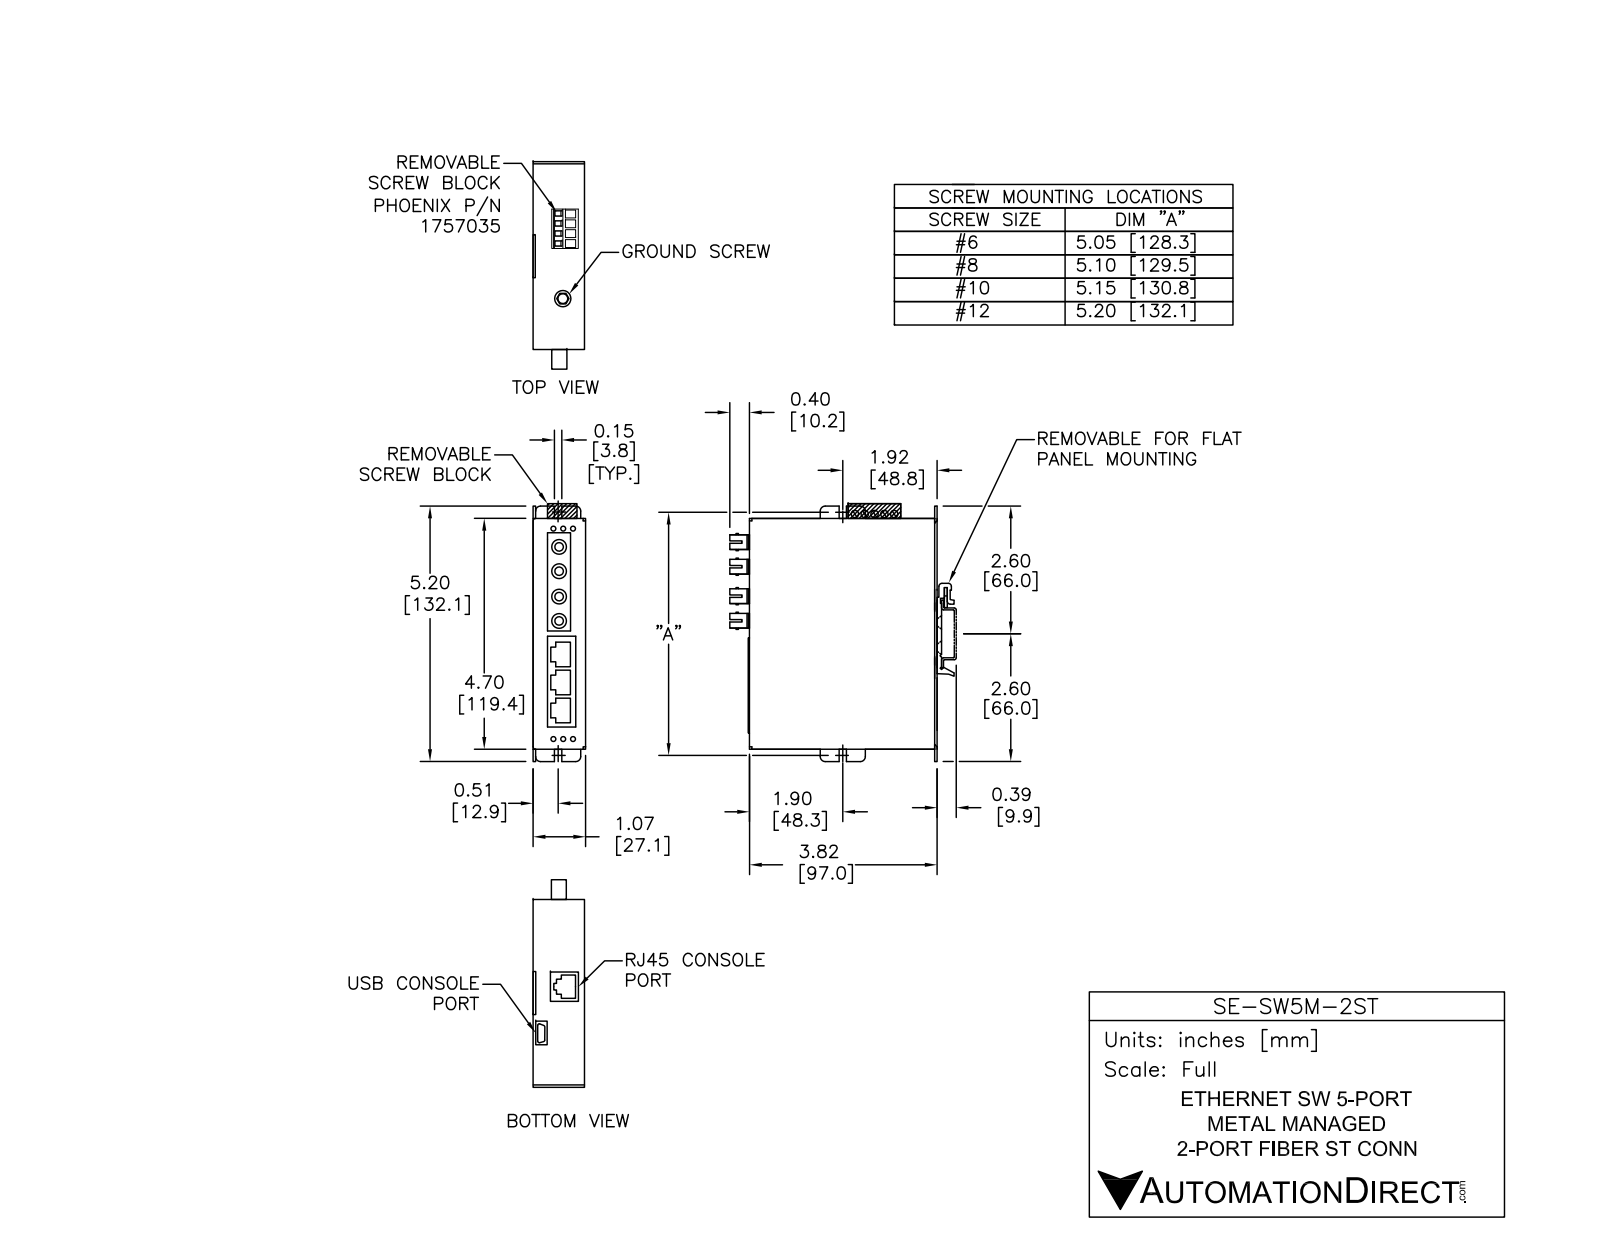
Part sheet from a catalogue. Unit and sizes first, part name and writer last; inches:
Units: inches
Overall size (bounding box): 5.38 × 4.656 × 1.07
Round holes (diameter × count): ⌀0.11 ×4, ⌀0.15 ×4, ⌀0.245 ×4, ⌀0.215 ×1
Round bosses / shafts (diameter × count): ⌀0.27 ×4, ⌀0.33 ×1
Partial cylindrical surfaces — rounded edges, fillets, slot ends (radius × count): R0.1 ×8, R0.03 ×7, R0.045 ×4, R0.07 ×4, R0.06 ×3, R0.075 ×1, R0.076 ×1, R0.125 ×1
Main face-to-face distances: 0.054, 1.07, 0.055, 1.015, 1.016, 0.055, 4.7, 3.82, 3.766, 3.765
Hole centre spacings: 0.185, 0.37, 0.164, 0.176, 0.341, 0.363, 0.465, 0.496
Volume: 19.38 in³ · Surface area: 105.2 in²
Bodies: 1 solid, 354 faces (304 planar, 50 cylindrical, 0 other)
Part name (STEP PRODUCT): SE-SW5M-2ST
STEP written by: SolidWorks 2011 (AUTOMOTIVE_DESIGN)
